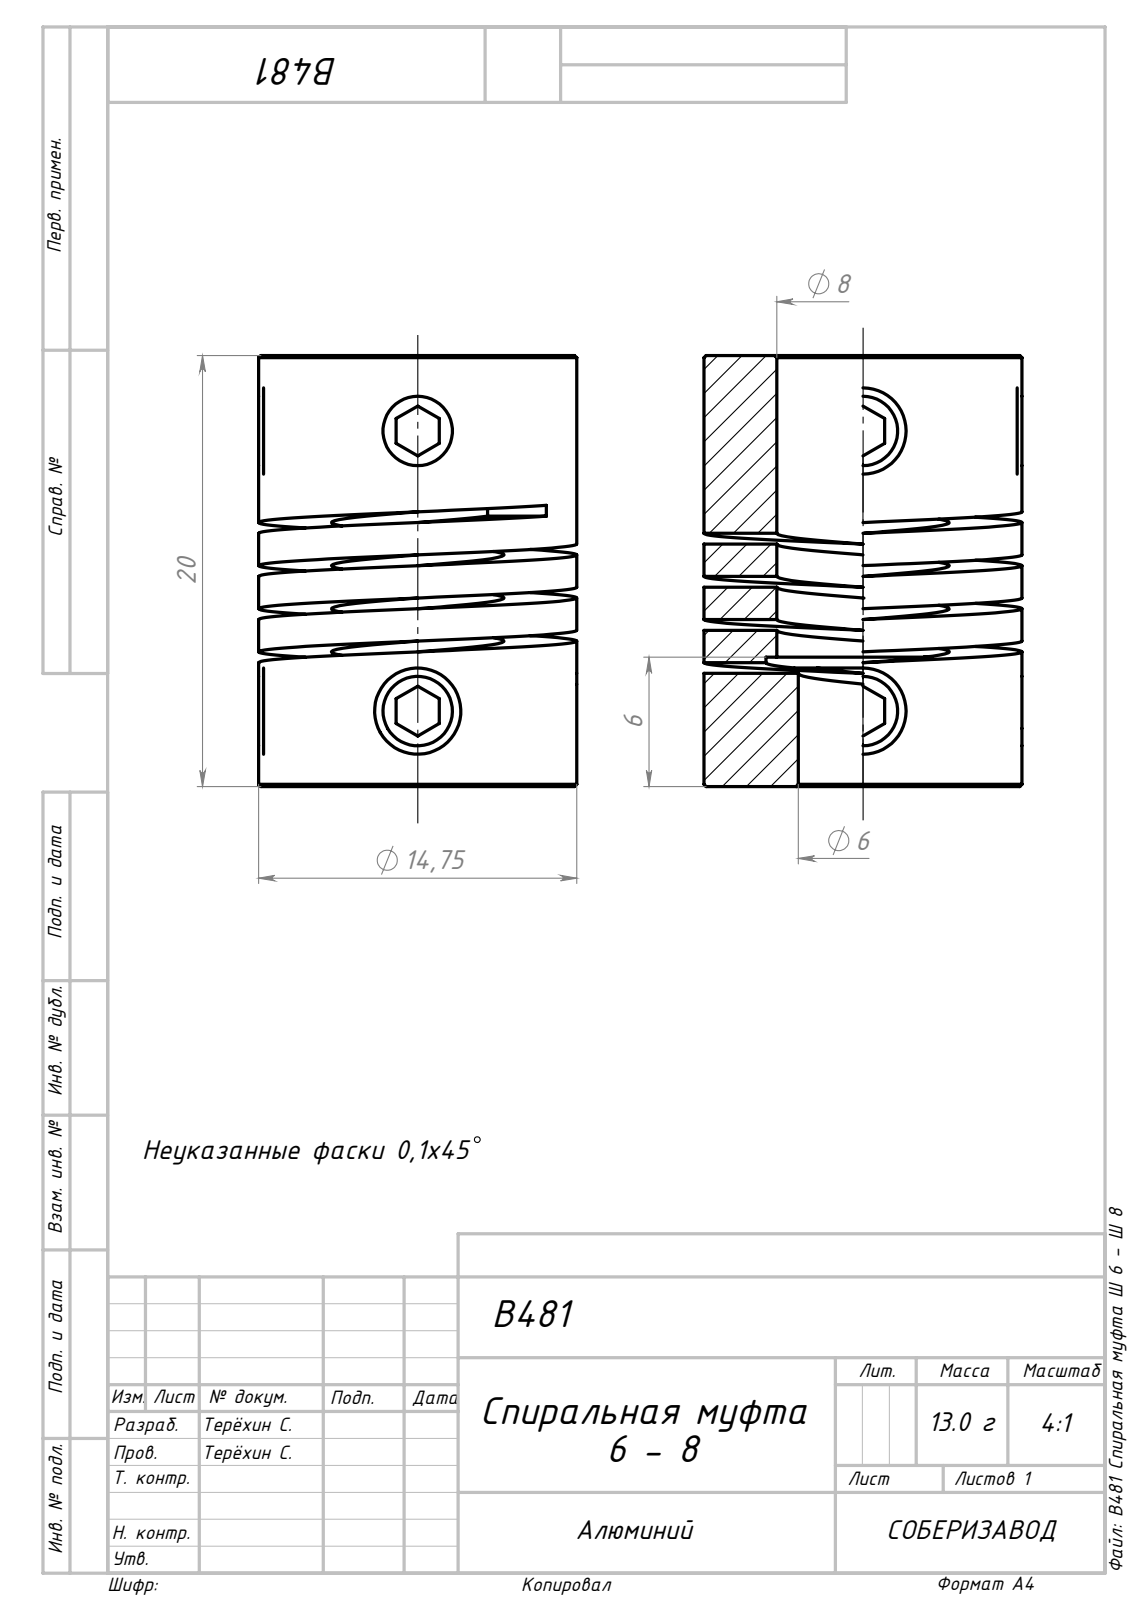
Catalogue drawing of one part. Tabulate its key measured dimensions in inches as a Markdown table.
| quantity | value |
| --- | --- |
| part name | Сборка1; B481 Спиральная муфта Ø 6 - Ø 8_00; socket set screw flat point_din_DIN 913 - M4 x 4-N |
| STEP written by | SolidWorks 2024 (AUTOMOTIVE_DESIGN) |
| units | inches |
| bodies | 5 solids, 107 faces (42 planar, 39 cylindrical, 26 other) |
| overall size | 0.787 × 0.787 × 0.787 |
| volume | 0.143 in³ |
| surface area | 4.497 in² |
| round holes (diameter × count) | 0.118 × 4, 0.236 × 1, 0.315 × 1, 0.354 × 1 |
| round bosses / shafts (diameter × count) | 0.157 × 4, 0.581 × 1 |
| main face-to-face distances | 0.787, 0.571, 0.217, 0.079, 0.157, 0.059, 0.098, 0.551, 0.02, 0.236 |
| hole center spacings | 0.512 |
